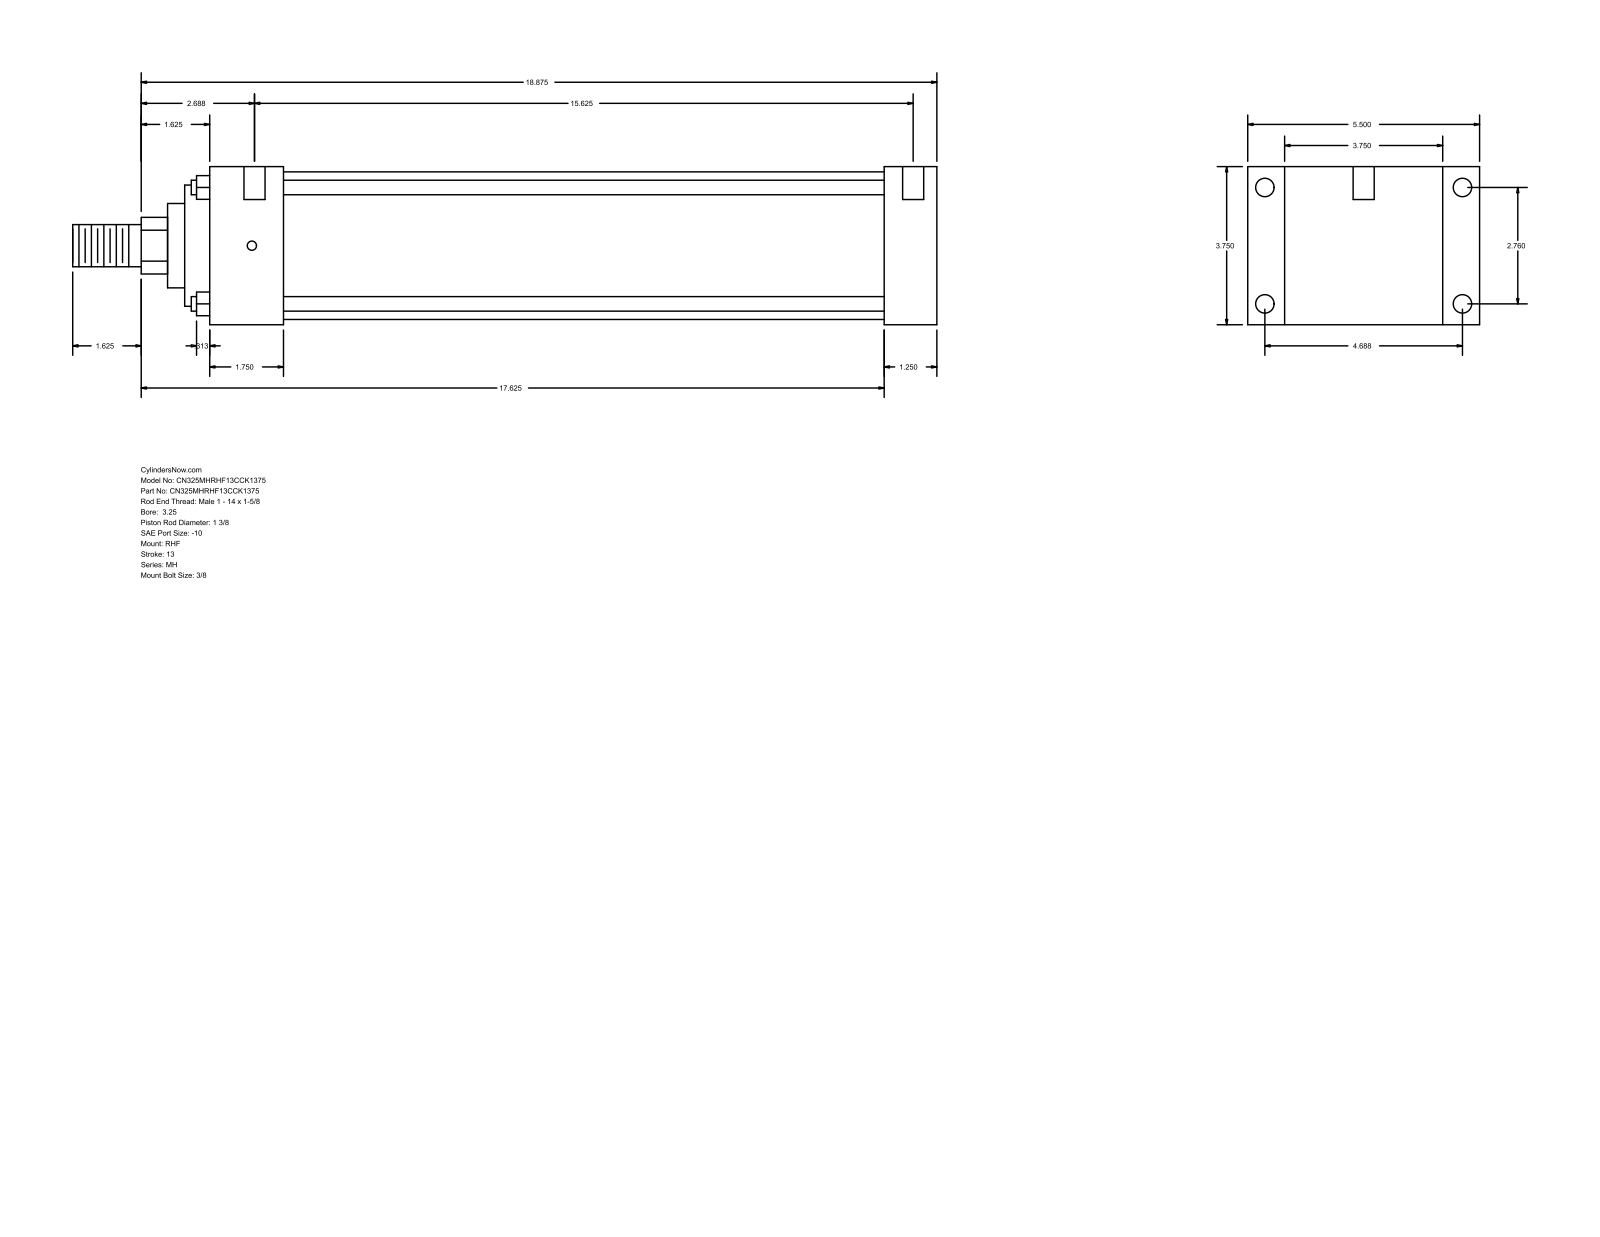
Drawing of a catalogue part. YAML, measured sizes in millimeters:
part_name: "MH_RHF__0325_1.375"
step_written_by: "GSSL Pune (CONFIG_CONTROL_DESIGN)"
units: millimeters
bodies: {solids: 0, faces: 90, planar: 61, cylindrical: 29, other: 0}
overall_size: [520.7, 139.7, 95.25]
round_holes:
  - {diameter: 5.56, count: 4}
  - {diameter: 11.13, count: 4}
  - {diameter: 12.7, count: 2}
round_bosses_or_shafts:
  - {diameter: 8.76, count: 4}
  - {diameter: 88.9, count: 1}
  - {diameter: 73.03, count: 1}
  - {diameter: 50.8, count: 1}
  - {diameter: 34.92, count: 1}
  - {diameter: 25.4, count: 1}
partial_cylinders:
  - {radius: 17.06, count: 1}
face_to_face_distances: [95.24, 31.75, 22.23, 117.47, 406.41, 438.16, 139.7, 44.45, 361.96, 393.71]
hole_center_spacings: [70.1, 119.06, 138.16, 403.23, 1.59, 4.76, 396.88, 398.47]
